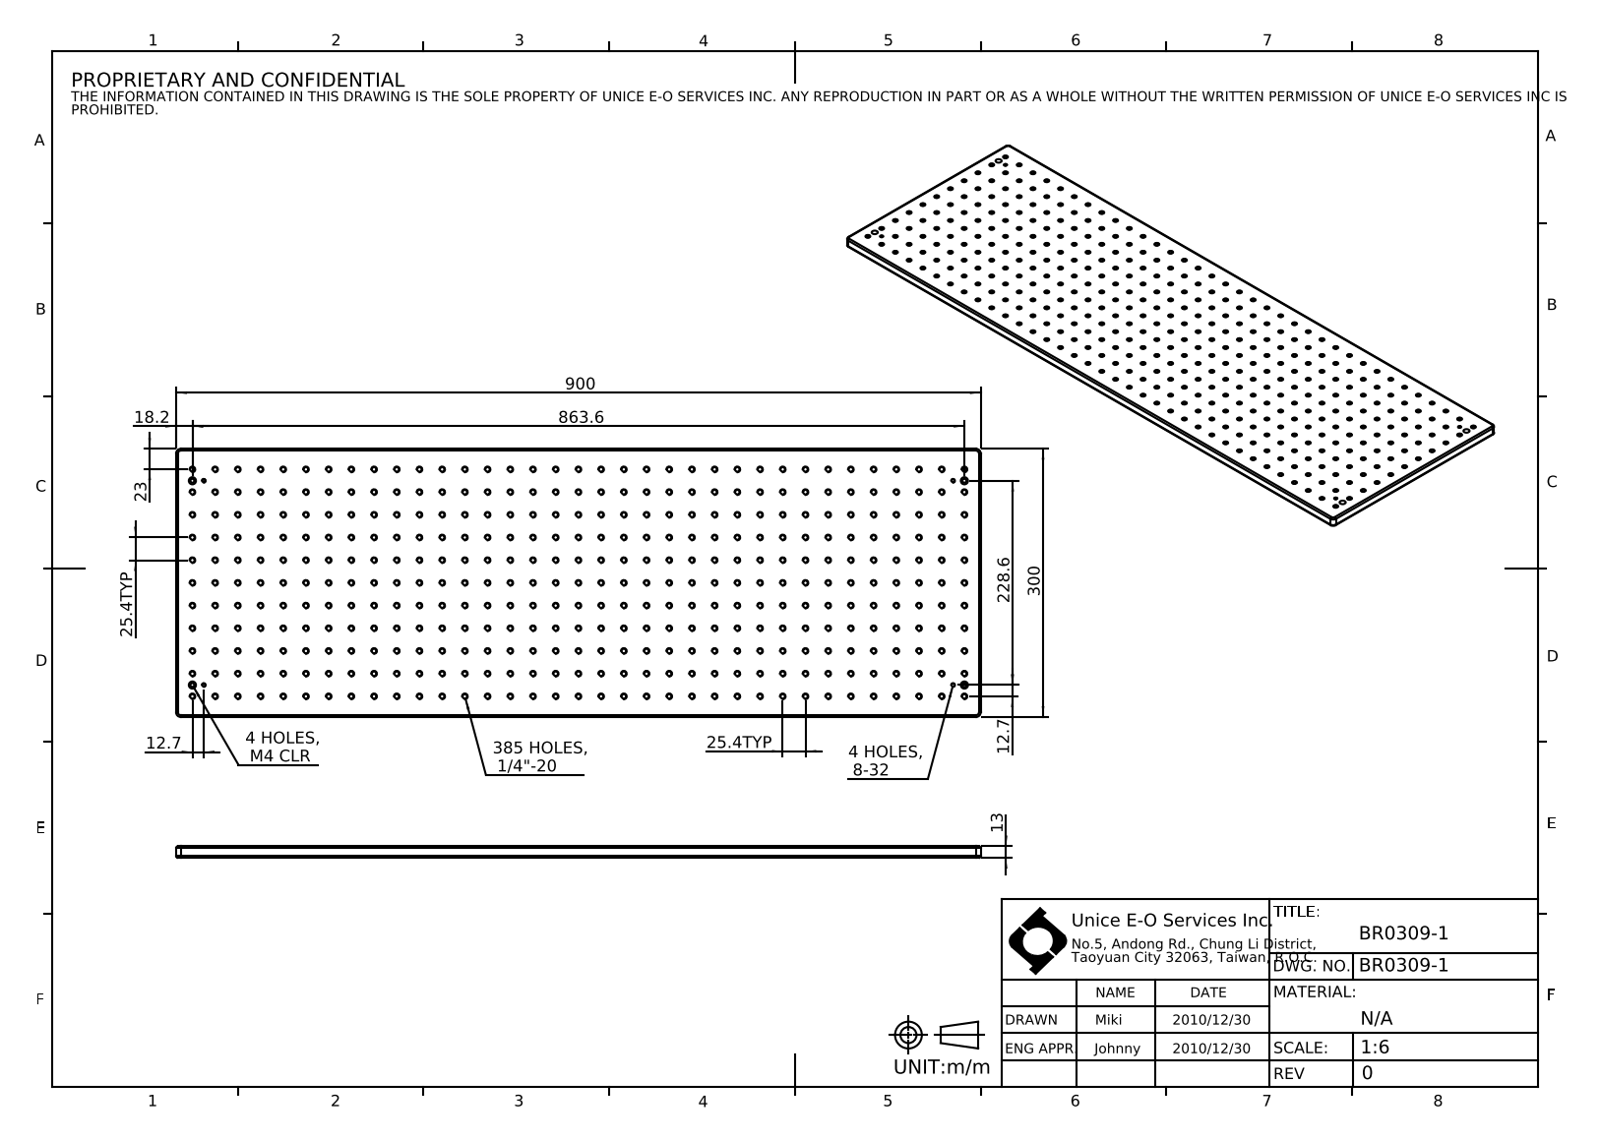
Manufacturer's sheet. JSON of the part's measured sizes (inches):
{"part_name": "BR0309-1", "step_written_by": "SolidWorks 2016 (CONFIG_CONTROL_DESIGN)", "units": "inches", "bodies": {"solids": 1, "faces": 824, "planar": 10, "cylindrical": 806, "other": 8}, "overall_size": [35.433, 11.811, 0.512], "volume_in3": 207.5, "surface_area_in2": 980.9, "round_holes": [[0.201, 385], [0.136, 4], [0.177, 4], [0.315, 4]], "partial_cylinders_radius": [[0.079, 8], [0.197, 4]], "face_to_face_distances": [0.512, 11.811, 35.433, 0.276, 0.236], "hole_center_spacings": [1, 2, 3, 4, 5, 9, 6, 7]}
